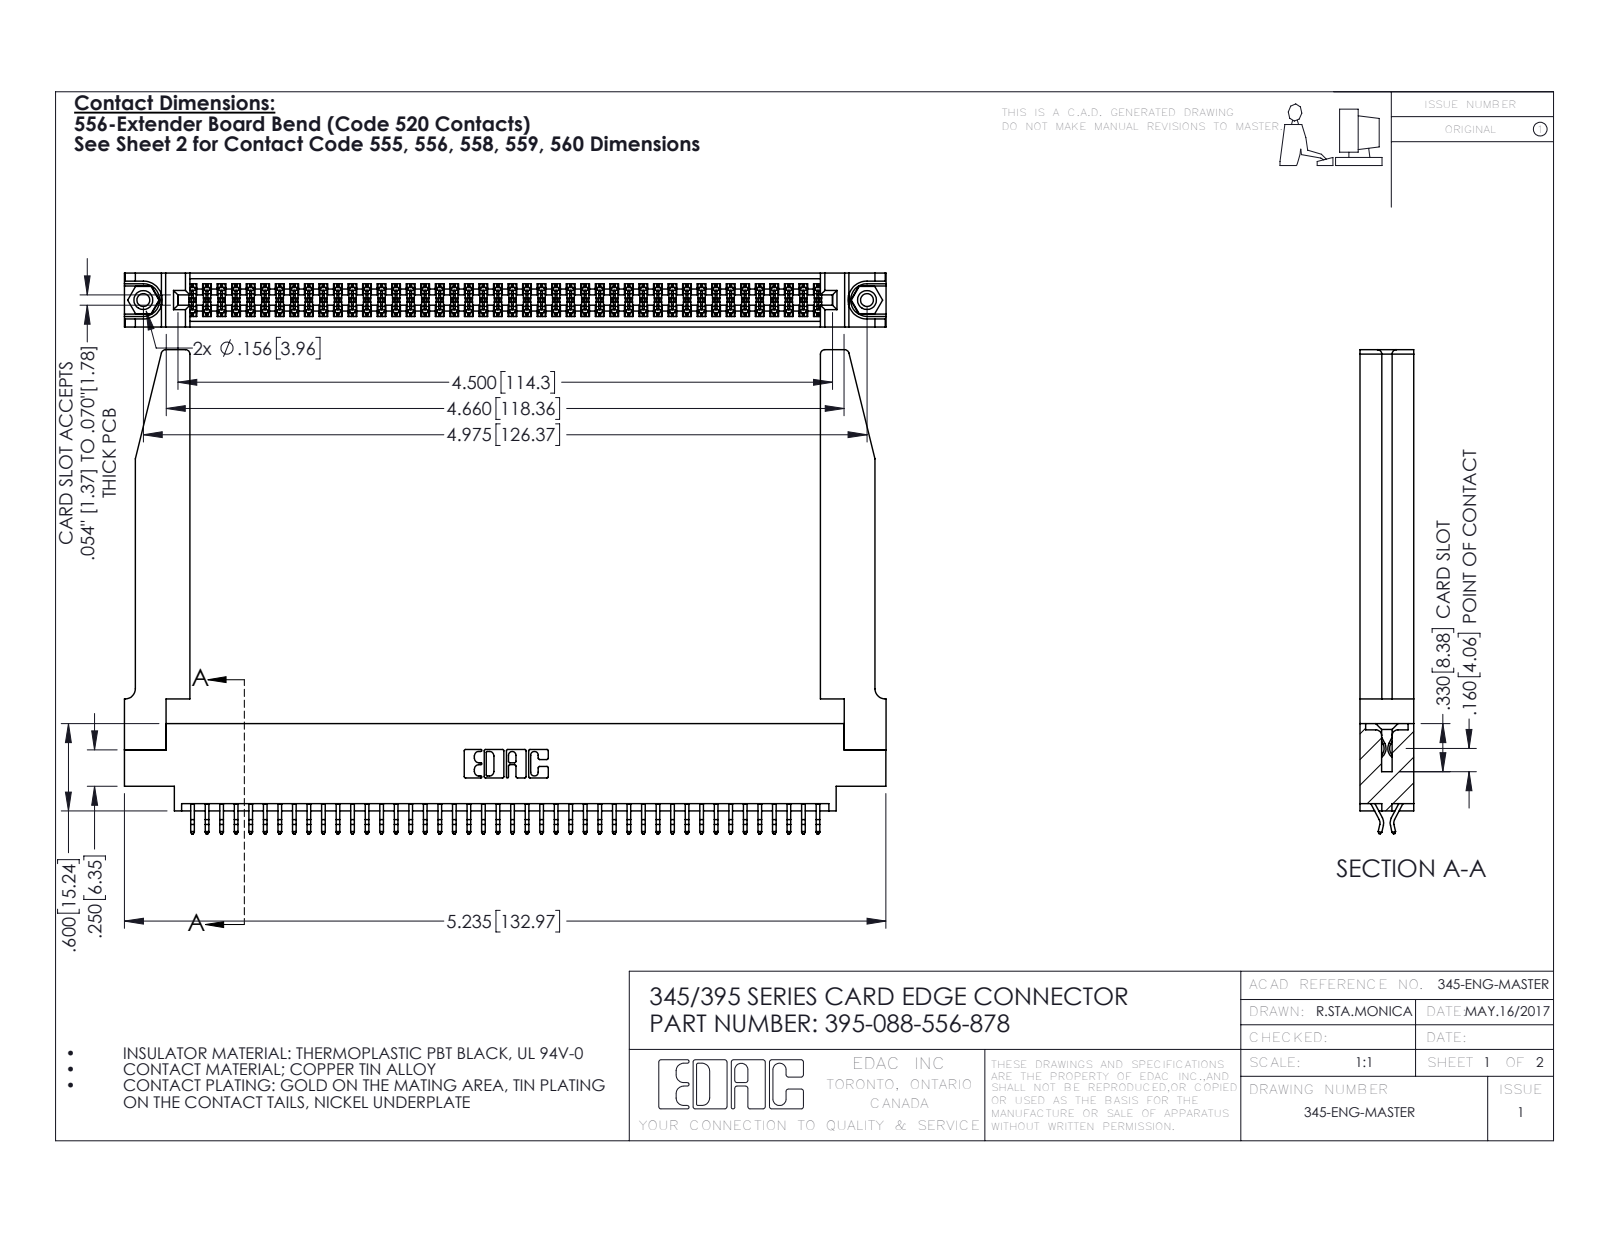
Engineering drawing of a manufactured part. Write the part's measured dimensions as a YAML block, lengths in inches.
part_name: "345 Part_0.170 Offset - 0.156 Dia-TH; 345-220-078_345-220-078; 345-250-001_345-250-001-102; 395-088-556-878 (+1 more)"
step_written_by: "SolidWorks 2016 (CONFIG_CONTROL_DESIGN)"
units: inches
bodies: {solids: 93, faces: 5292, planar: 3482, cylindrical: 1758, other: 52}
overall_size: [5.236, 3.327, 0.37]
volume: 1.257
surface_area: 40.14
round_holes:
  - {diameter: 0.089, count: 2}
  - {diameter: 0.125, count: 2}
  - {diameter: 0.156, count: 2}
  - {diameter: 0.064, count: 1}
round_bosses_or_shafts:
  - {diameter: 0.155, count: 2}
partial_cylinders:
  - {radius: 0.006, count: 132}
  - {radius: 0.01, count: 22}
  - {radius: 0.03, count: 8}
  - {radius: 0.007, count: 6}
  - {radius: 0.031, count: 6}
  - {radius: 0.026, count: 3}
  - {radius: 0.01, count: 2}
  - {radius: 0.014, count: 2}
face_to_face_distances: [0.37, 0.072, 0.298, 0.025, 0.2, 0.098, 0.272, 0.225, 0.175, 0.148]
hole_center_spacings: [0.27, 4.739, 4.975]
